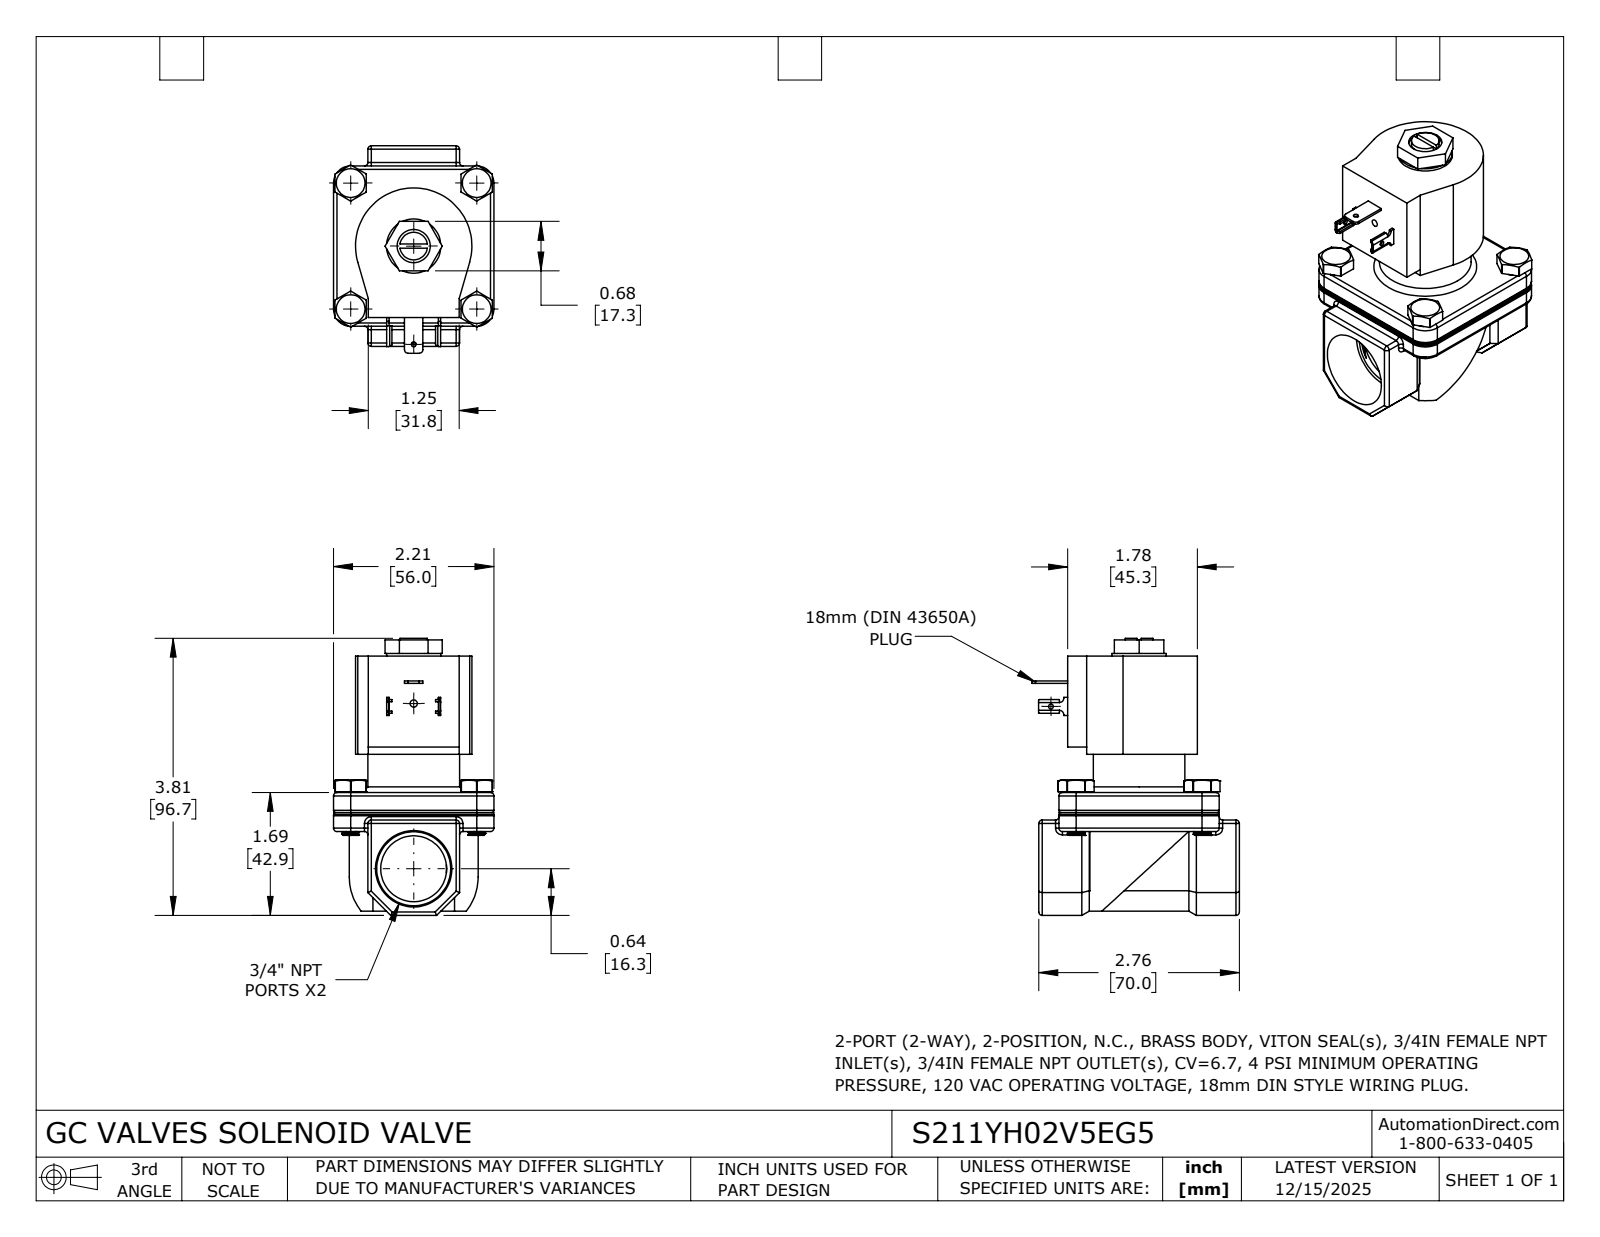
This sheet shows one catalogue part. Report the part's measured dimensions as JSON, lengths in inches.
{"part_name": "S211YH02V5EG5", "step_written_by": "SolidWorks 2024 (CONFIG_CONTROL_DESIGN)", "units": "inches", "bodies": {"solids": 1, "faces": 402, "planar": 195, "cylindrical": 131, "other": 76}, "overall_size": [3.809, 2.851, 2.205], "volume_in3": 9.438, "surface_area_in2": 43.49, "round_holes": [[0.066, 1], [0.067, 1], [0.1, 1], [0.456, 1], [0.906, 1]], "round_bosses_or_shafts": [[0.407, 4], [0.242, 4], [1.26, 1], [0.746, 1], [0.38, 1]], "partial_cylinders_radius": [[0.047, 34], [0.006, 4], [0.031, 4], [0.041, 4], [0.234, 4], [0.236, 4], [0.05, 2], [0.06, 2]], "face_to_face_distances": [0.059, 1.873, 0.472, 1.732, 0.537, 2.41, 2.205, 1.094, 1.631, 3.504], "hole_center_spacings": [1.35, 2.271]}
